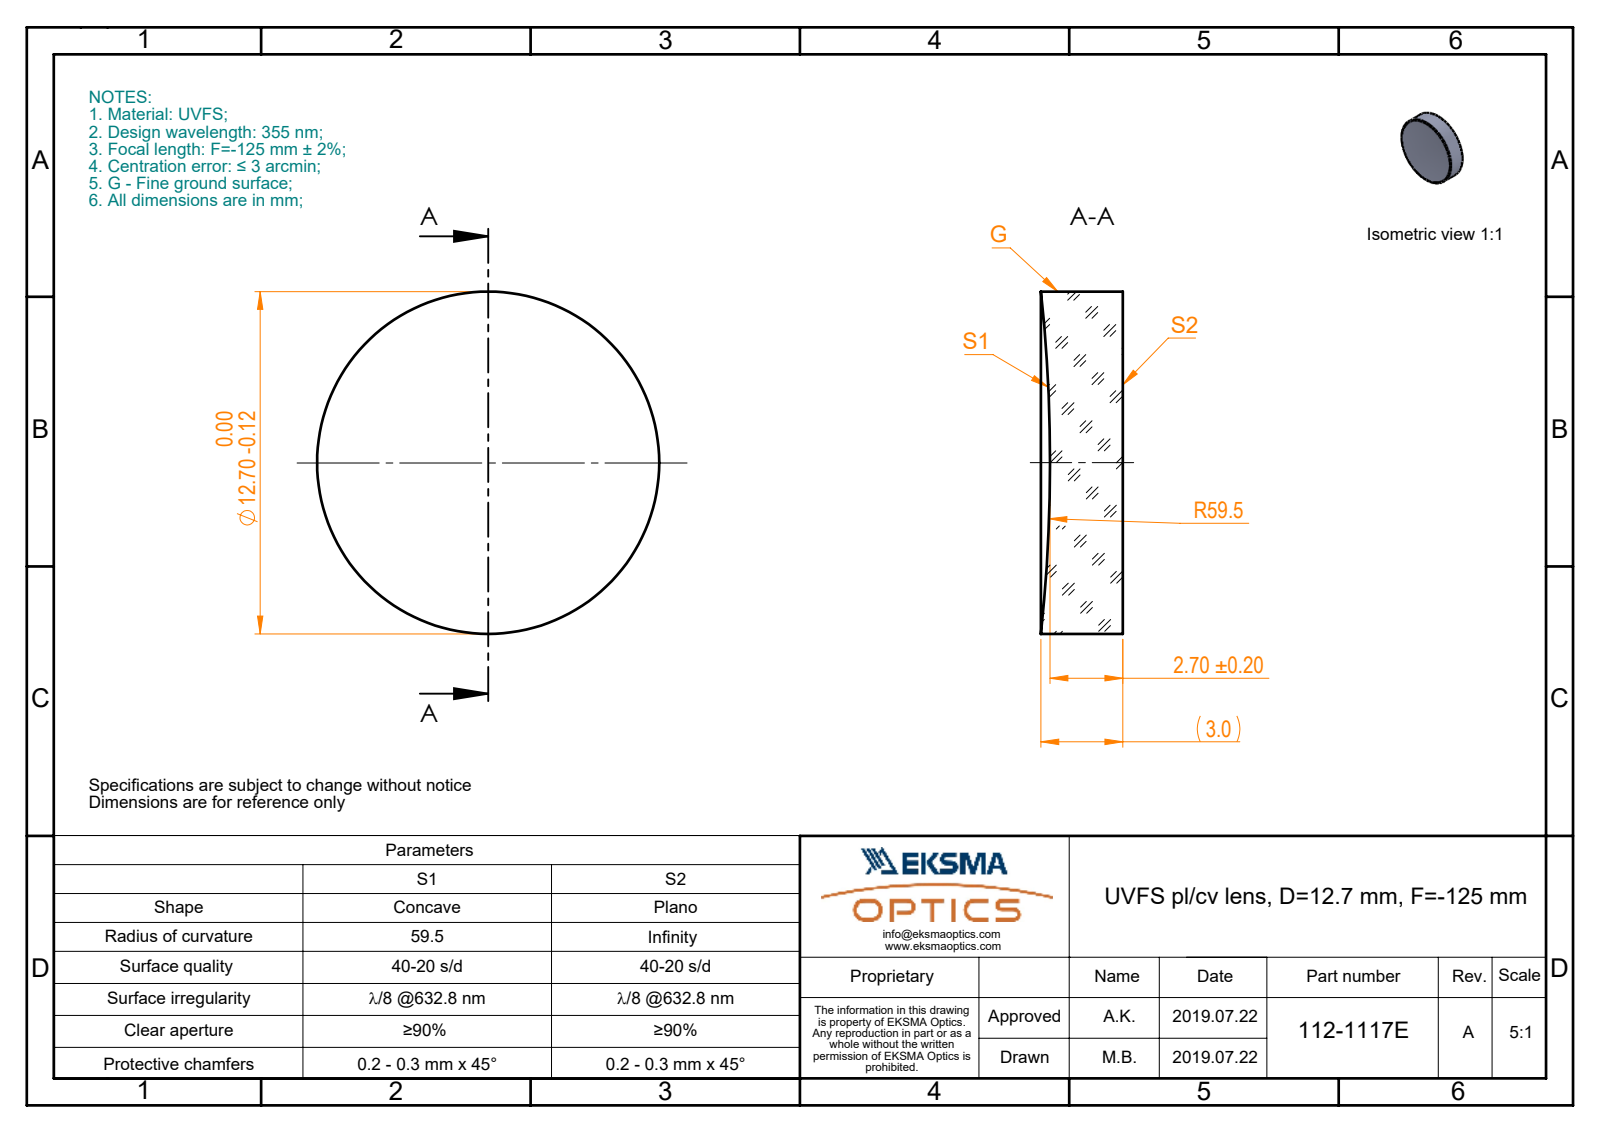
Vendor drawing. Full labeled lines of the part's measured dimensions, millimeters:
Part name (STEP PRODUCT): 112-1117E UVFS pl-cv 12.7 F-125
STEP written by: SolidWorks 2017 (CONFIG_CONTROL_DESIGN)
Units: millimetres
Bodies: 1 solid, 5 faces (1 planar, 2 cylindrical, 2 other)
Overall size (bounding box): 12.7 × 12.7 × 3.04
Volume: 364 mm³ · Surface area: 375 mm²
Round bosses / shafts (diameter × count): ⌀12.7 ×1
